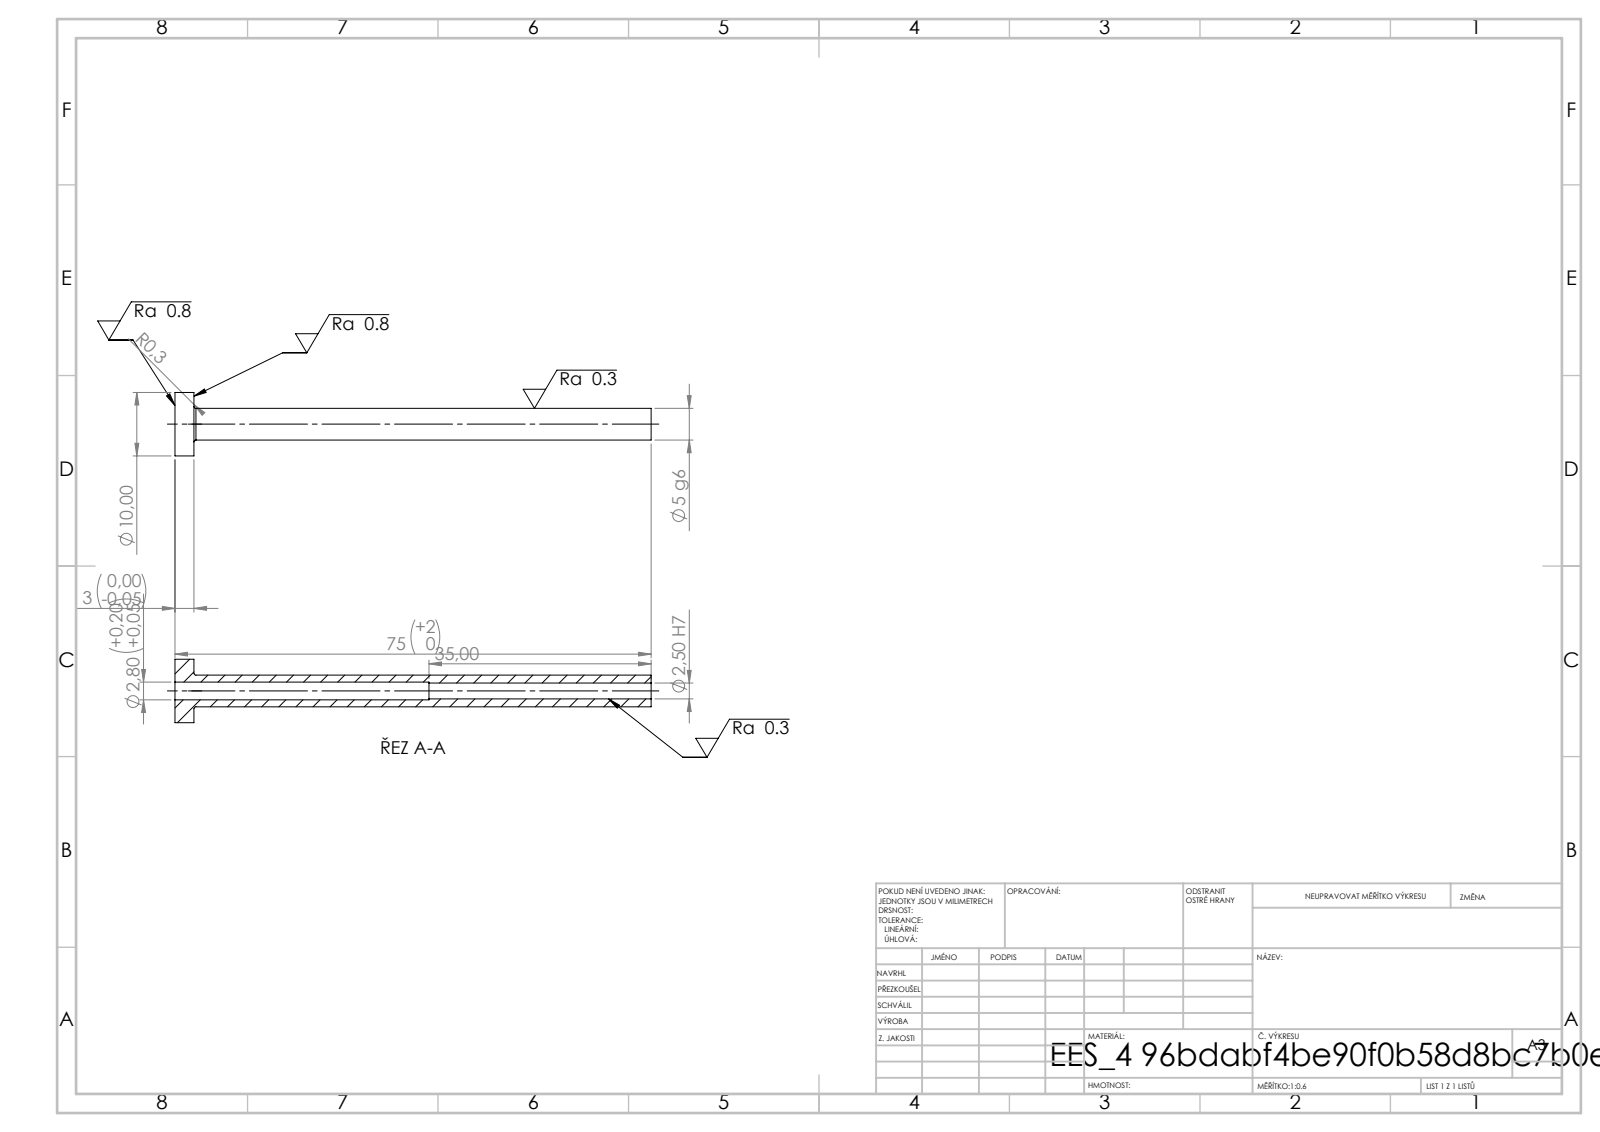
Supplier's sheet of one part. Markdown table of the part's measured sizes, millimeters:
| quantity | value |
| --- | --- |
| STEP written by | SolidWorks 2019 (CONFIG_CONTROL_DESIGN) |
| units | millimeters |
| bodies | 1 solid, 14 faces (4 planar, 8 cylindrical, 2 other) |
| overall size | 75 × 10 × 10 |
| volume | 1 232 mm³ |
| surface area | 1 997 mm² |
| round holes (diameter × count) | 2.5 × 1, 2.8 × 1 |
| round bosses / shafts (diameter × count) | 10 × 1, 5 × 1 |
| main face-to-face distances | 3, 75, 72, 40, 37, 35 |
